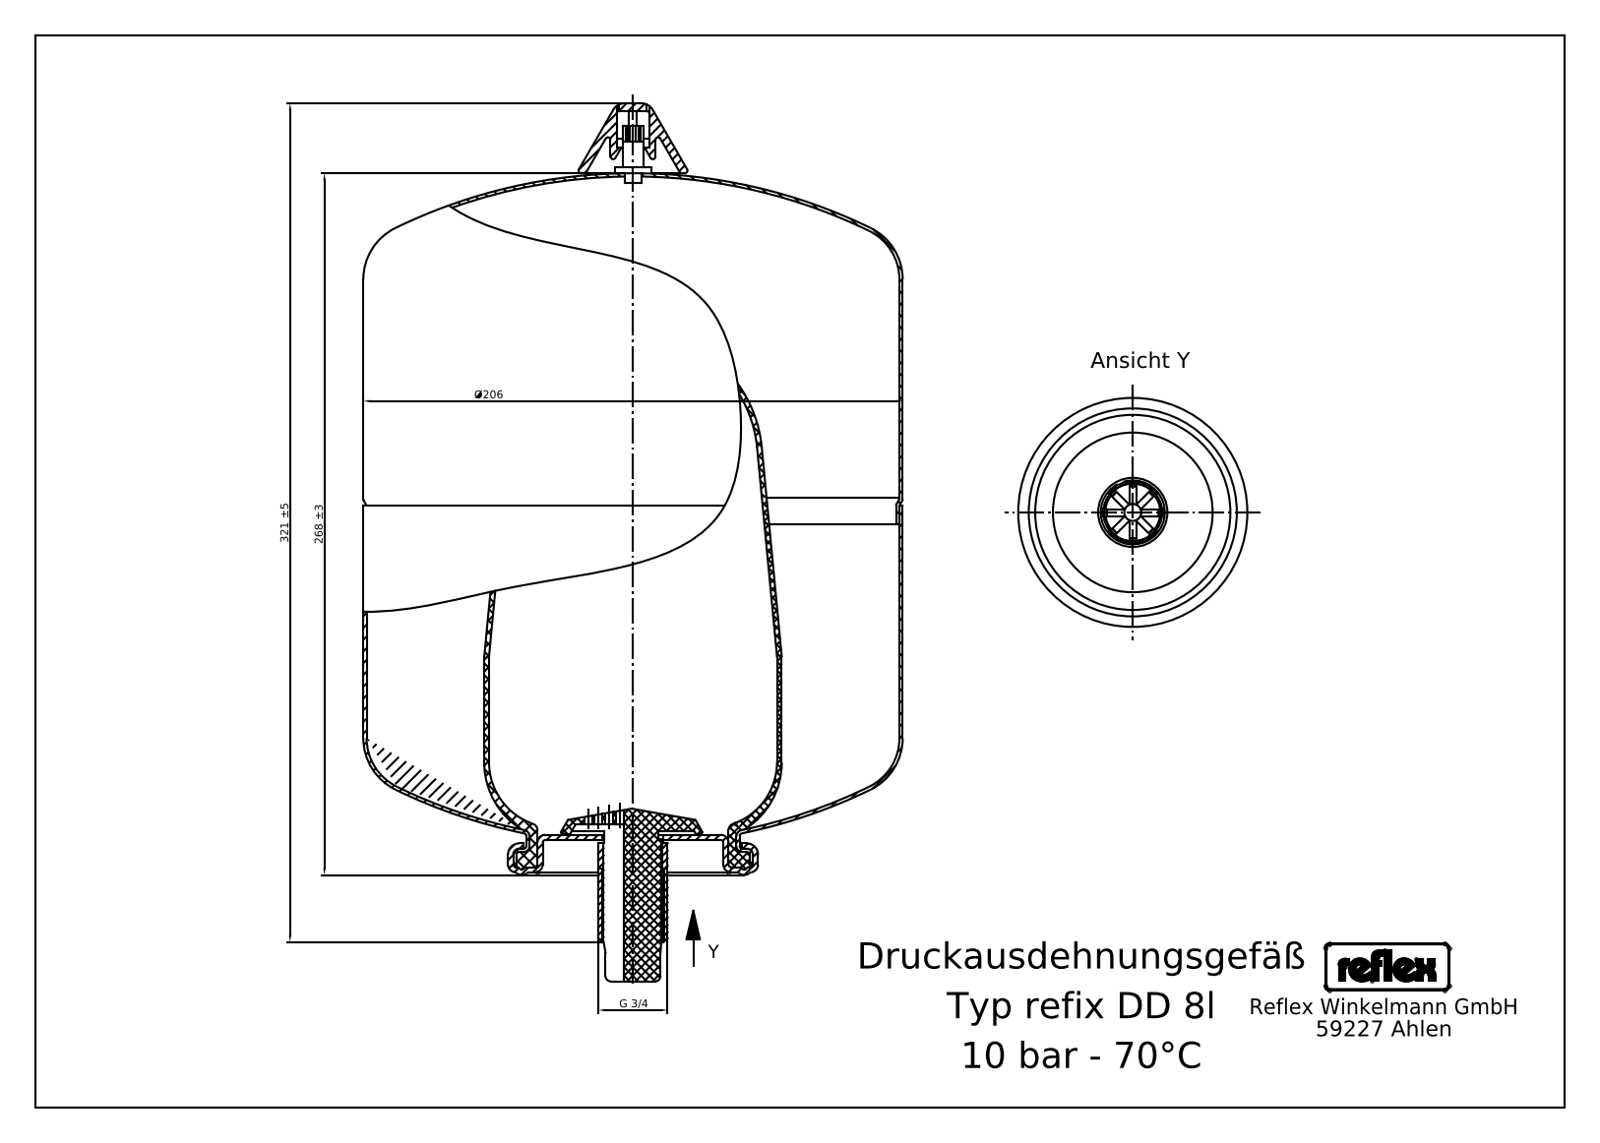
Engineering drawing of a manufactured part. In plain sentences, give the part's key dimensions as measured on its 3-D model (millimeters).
Its 3-D file was written by "Mechanical Desktop 2008 (CONFIG_CONTROL_DESIGN)". It is 14 solids with 217 faces: 129 planar, 46 cylindrical and 42 other. Overall it measures 337 by 206.32 by 206 millimeters. Its volume is 7 835 000 cubic millimeters and its surface area 381 893 square millimeters. Round holes: 1 of diameter 14.1, 1 of diameter 18.9. Round bosses or shafts: 1 of diameter 206, 1 of diameter 96, 1 of diameter 82, 1 of diameter 26.9, 1 of diameter 17.1, 1 of diameter 9, 1 of diameter 6. Partial cylindrical surfaces (rounded edges, fillets, slot ends): 4 of radius 1.12, 3 of radius 0.45, 2 of radius 0.77, 2 of radius 1.35, 2 of radius 1.85, 2 of radius 1.88, 2 of radius 2.54, 1 of radius 0.56. The main face-to-face distances are 179, 33, 212, 46, 13, 225, 1.5, 6, 7, 39.
